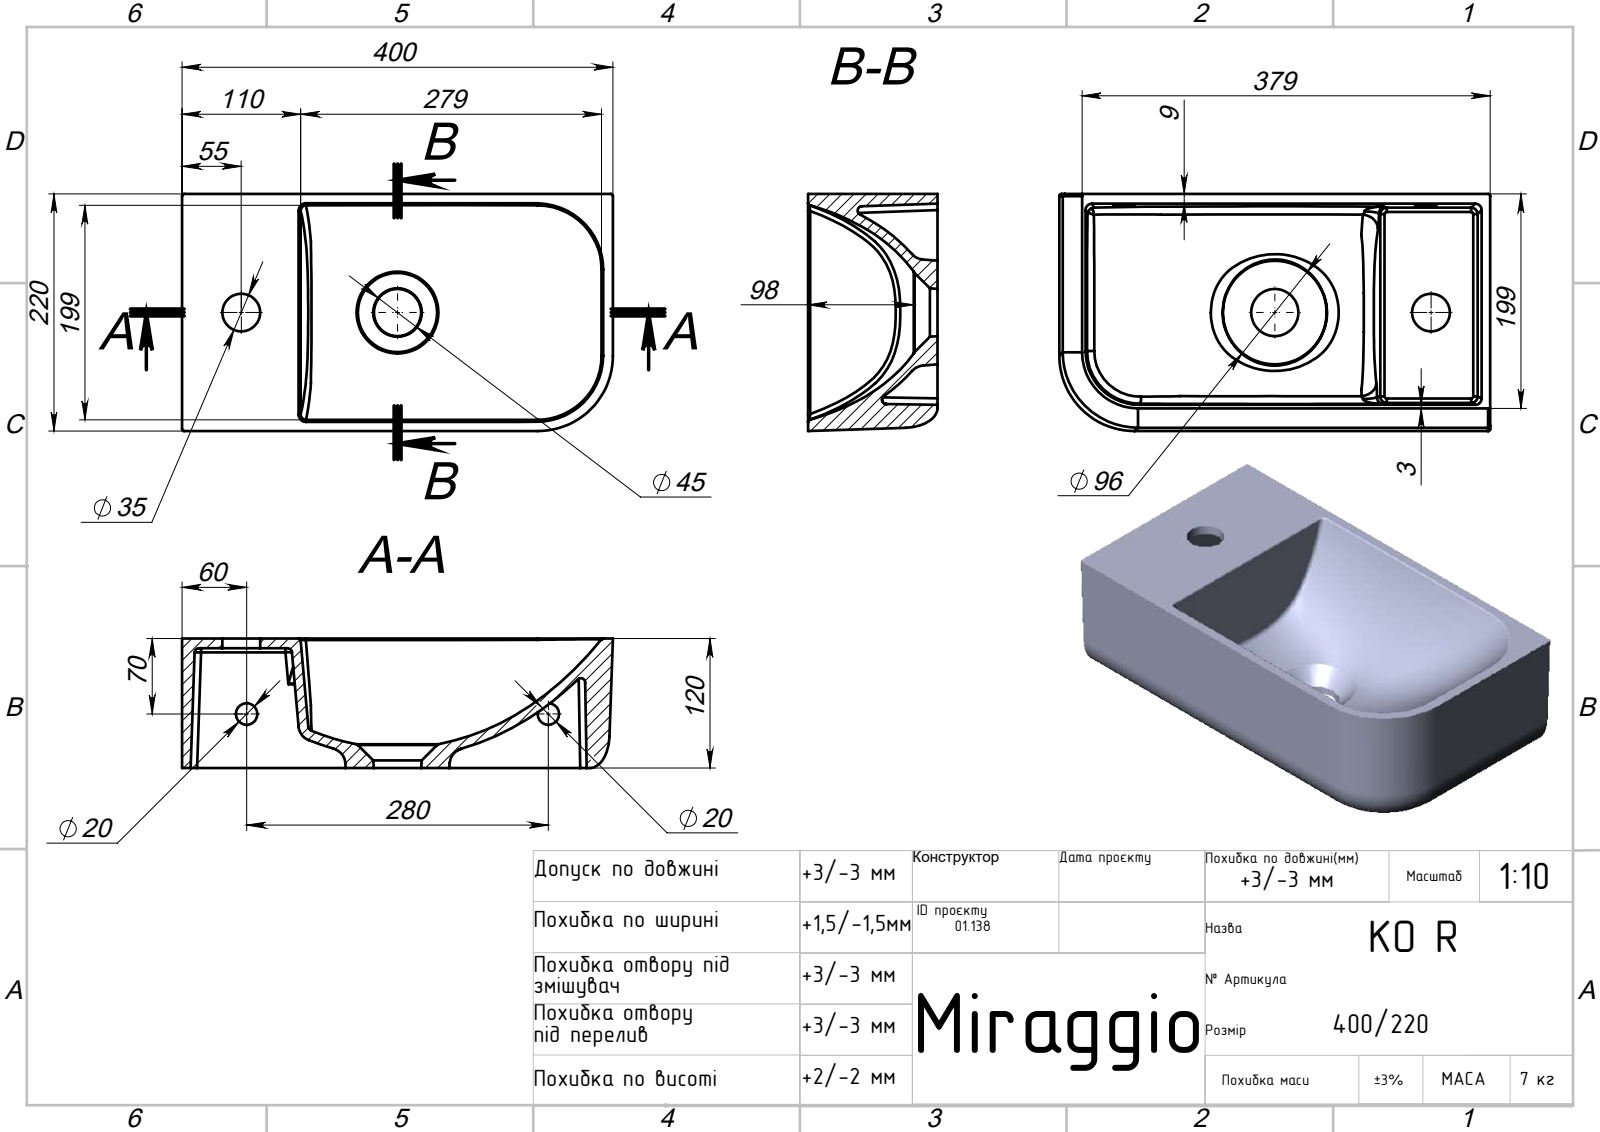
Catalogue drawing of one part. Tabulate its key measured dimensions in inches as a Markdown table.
| quantity | value |
| --- | --- |
| part name | Ko R |
| STEP written by | SolidWorks 2020 (AUTOMOTIVE_DESIGN) |
| units | inches |
| bodies | 1 solid, 68 faces (17 planar, 17 cylindrical, 34 other) |
| overall size | 15.748 × 8.661 × 4.724 |
| volume | 183.3 in³ |
| surface area | 713.2 in² |
| round holes (diameter × count) | 0.787 × 2, 1.378 × 1 |
| partial cylindrical surfaces (radius × count) | 0.236 × 5, 0.079 × 4, 0.157 × 4, 2.756 × 1 |
| main face-to-face distances | 8.133, 0.354, 15.252, 4.37, 4.724, 14.915, 7.829 |
| hole center spacings | 11.024 |
